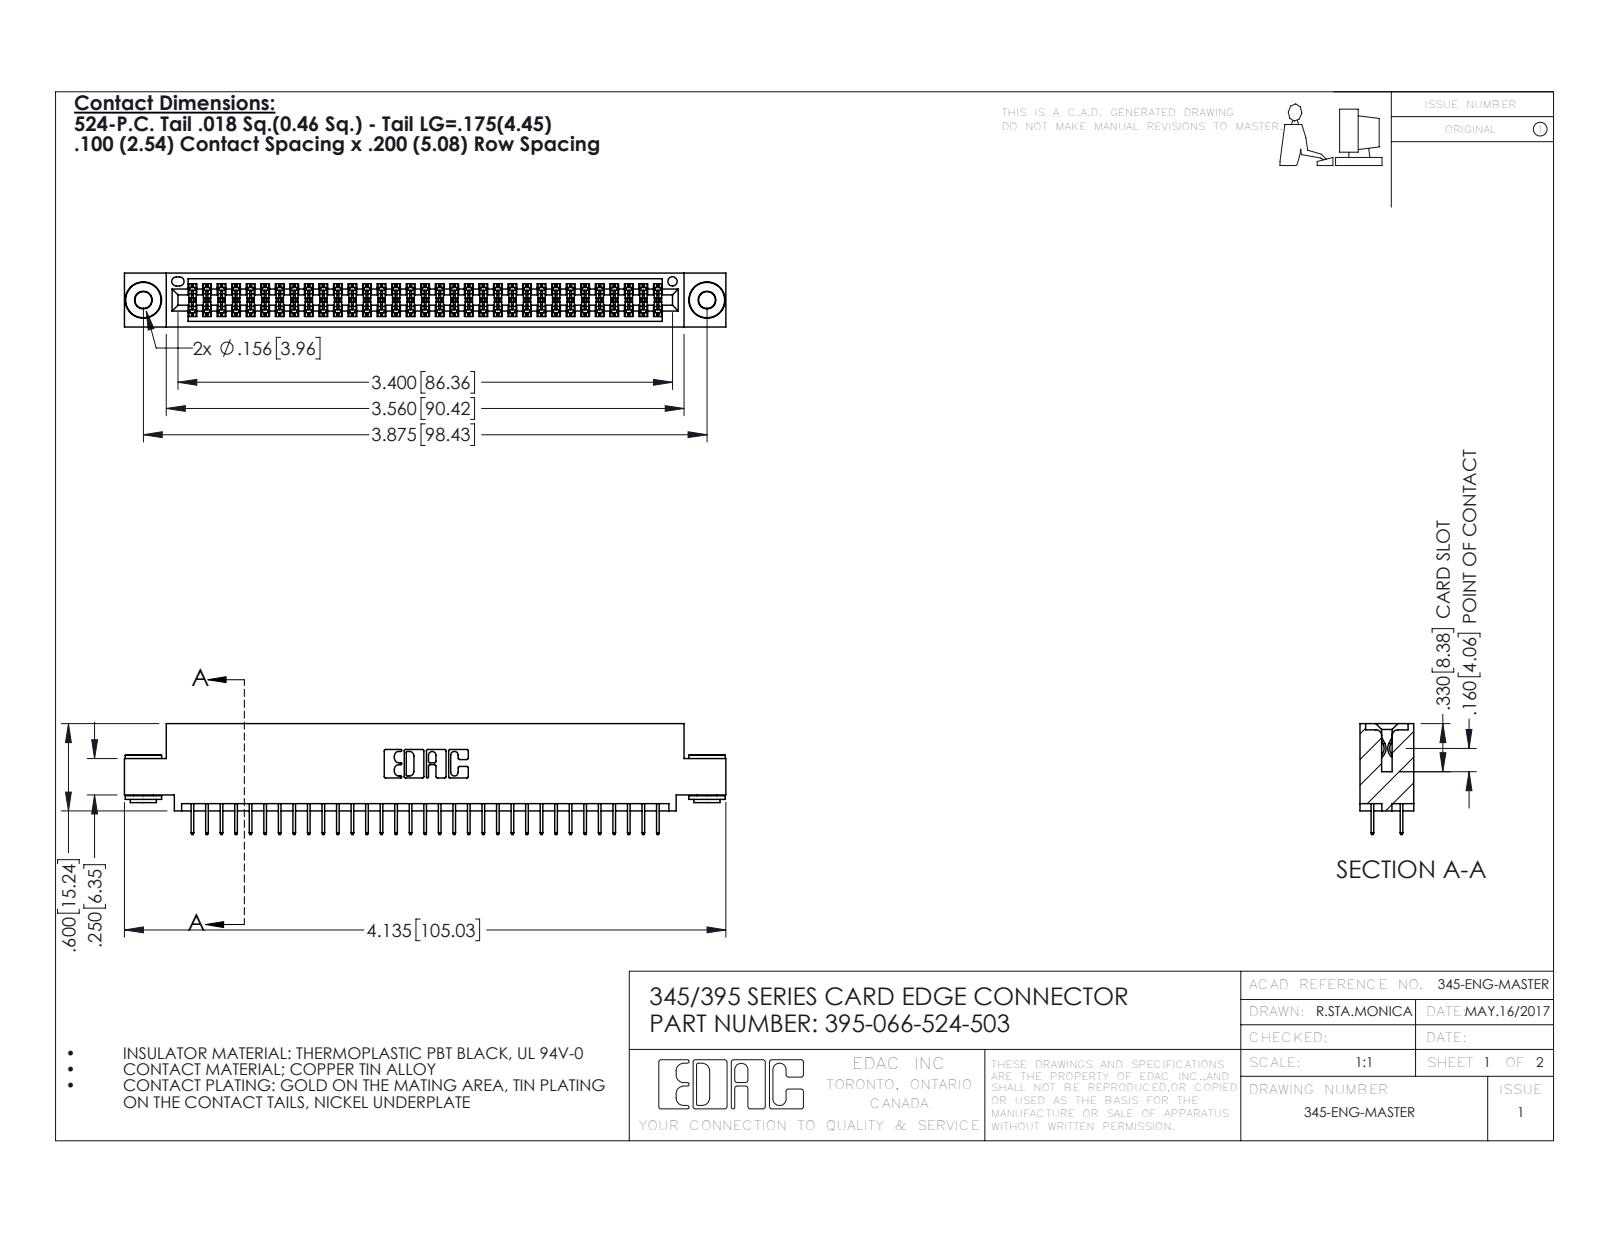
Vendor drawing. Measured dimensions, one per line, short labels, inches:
name: 345 Part_0.110 Offset - 0.156 Dia-TH; 345-250-002_345-250-002-102; 395-066-524-503; 345-292-001_345-293-124
written by: SolidWorks 2016 (CONFIG_CONTROL_DESIGN)
unit: in
bodies: 69 solids, 3732 faces (2668 planar, 1056 cylindrical, 8 other)
size: 4.135 × 0.762 × 0.37
volume: 0.608 in³; area: 22.61 in²
holes: 2× ⌀0.116, 2× ⌀0.156, 1× ⌀0.064
bosses: 2× ⌀0.25, 2× ⌀0.18, 2× ⌀0.136
rounds: 99× R0.006, 22× R0.01, 6× R0.007, 6× R0.031, 3× R0.026, 2× R0.014, 2× R0.019, 2× R0.022
face distances: 0.072, 0.298, 0.2, 0.37, 0.025, 0.098, 0.272, 0.225, 0.072, 0.175
hole spacings: 0.27, 3.64, 3.875
